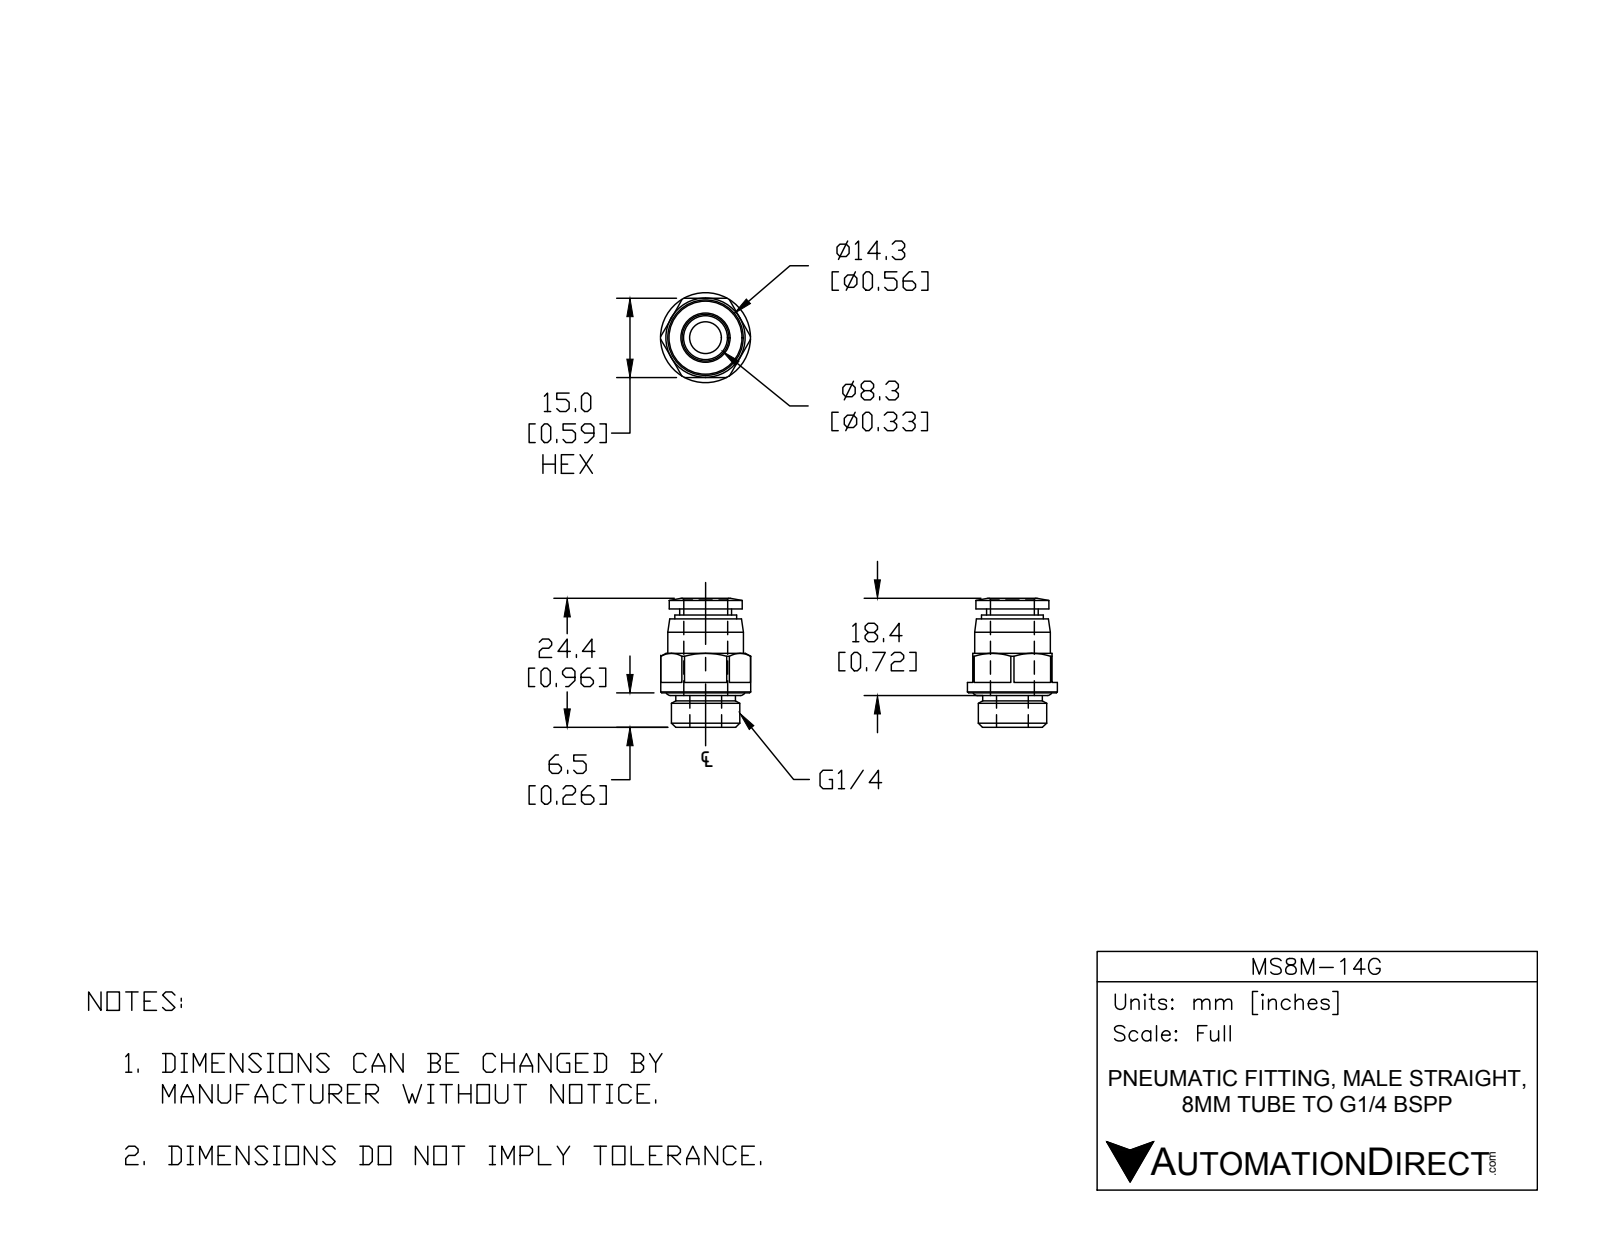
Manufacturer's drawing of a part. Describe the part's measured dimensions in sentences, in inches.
The part is named "MS8M-14G". Its 3-D file was written by "SolidWorks 2018 (AUTOMOTIVE_DESIGN)". It is 2 solids with 64 faces: 21 planar, 18 cylindrical and 25 other. Overall it measures 0.961 by 0.669 by 0.669 inches. Its volume is 0.161 cubic inches and its surface area 3.907 square inches. Round holes: 1 of diameter 0.236, 1 of diameter 0.327. Round bosses or shafts: 1 of diameter 0.669, 1 of diameter 0.563, 1 of diameter 0.543, 1 of diameter 0.51, 1 of diameter 0.461, 1 of diameter 0.445, 1 of diameter 0.386. The main face-to-face distances are 0.591, 0.882, 0.075, 0.571, 0.807, 0.256, 0.551, 0.335, 0.472, 0.547.
